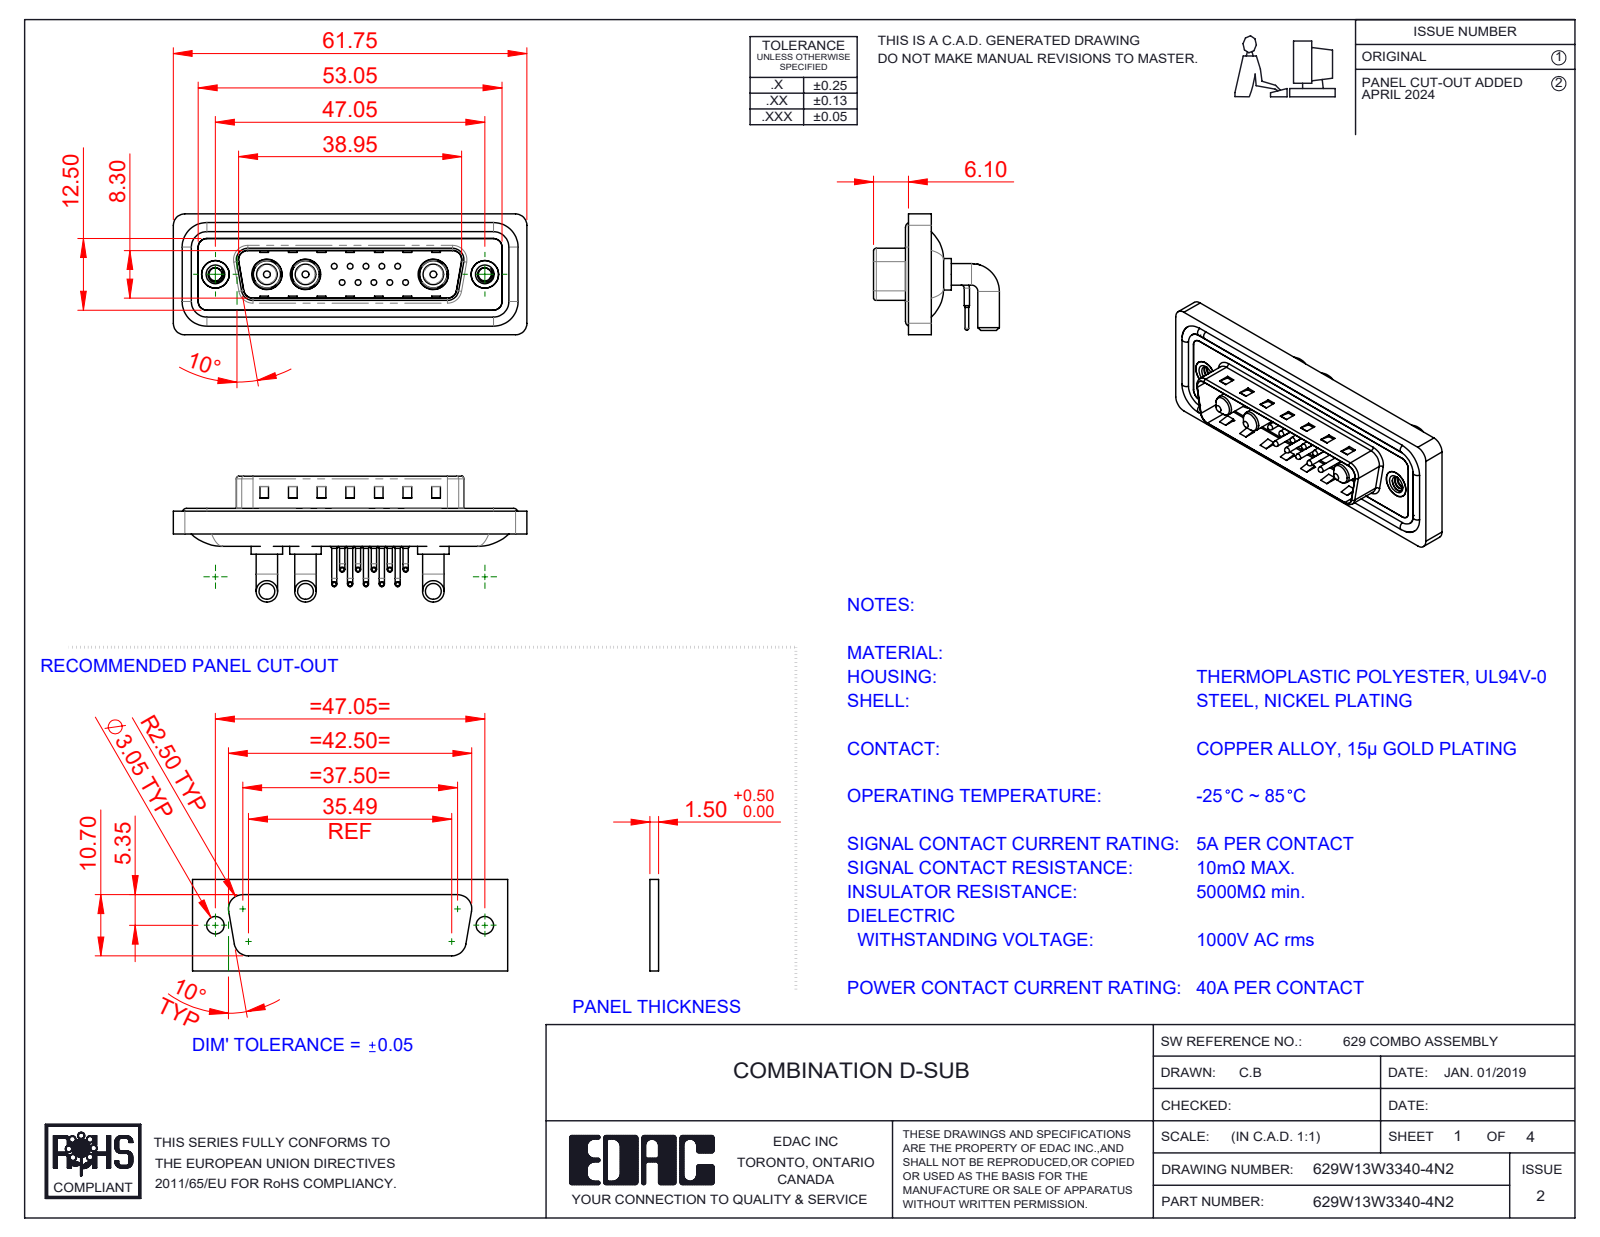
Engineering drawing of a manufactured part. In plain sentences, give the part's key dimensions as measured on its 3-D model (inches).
The part is named "629Combo Threaded Rivet_2; 629Combo Contact Row 2; 629Combo Waterproof Housing_25 Contacts; 629Combo Shell Rear_25 Contacts (+5 more)". Its 3-D file was written by "SolidWorks 2023 (CONFIG_CONTROL_DESIGN)". It is 23 solids with 1712 faces: 879 planar, 611 cylindrical and 222 other. Overall it measures 2.431 by 0.865 by 0.831 inches. Its volume is 0.478 cubic inches and its surface area 19.57 square inches. Round holes: 10 of diameter 0.03, 10 of diameter 0.063, 10 of diameter 0.079, 3 of diameter 0.191, 3 of diameter 0.209, 2 of diameter 0.089, 2 of diameter 0.157, 2 of diameter 0.189, 2 of diameter 0.197. Round bosses or shafts: 20 of diameter 0.035, 10 of diameter 0.059, 10 of diameter 0.039, 10 of diameter 0.026, 6 of diameter 0.148, 4 of diameter 0.063, 3 of diameter 0.217, 3 of diameter 0.205. Partial cylindrical surfaces (rounded edges, fillets, slot ends): 18 of radius 0.059, 18 of radius 0.079, 10 of radius 0.04, 8 of radius 0.02, 8 of radius 0.063, 4 of radius 0.01, 4 of radius 0.024, 4 of radius 0.026. The main face-to-face distances are 0.016, 0.114, 0.031, 0.161, 0.043, 0.083, 0.063, 0.177, 0.098, 0.059. The hole center spacings are 0.124, 0.109, 0.198, 0.218, 0.295, 0.198, 0.327, 0.398.
